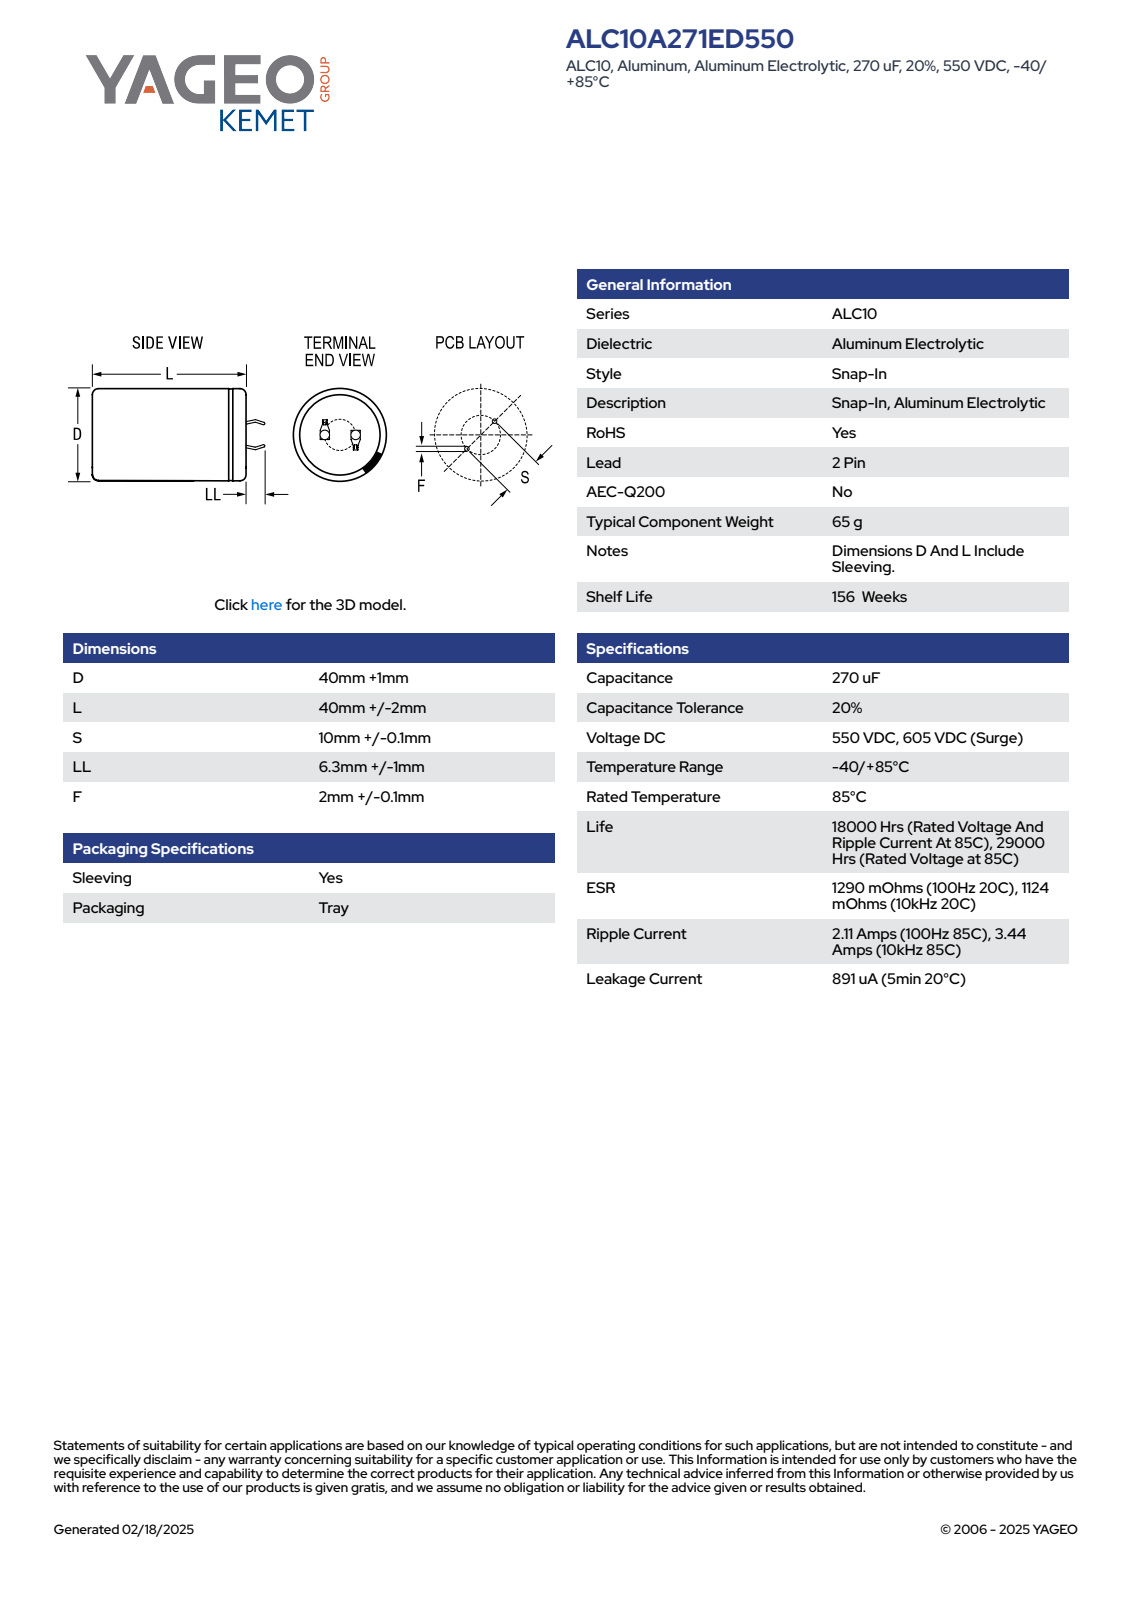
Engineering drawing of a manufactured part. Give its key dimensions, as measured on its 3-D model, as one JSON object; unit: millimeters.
{"part_name": "CARS_K2P_40X40_D41L42S10LL7.3F2.1", "step_written_by": "SolidWorks 2014 (AUTOMOTIVE_DESIGN)", "units": "millimeters", "bodies": {"solids": 1, "faces": 100, "planar": 52, "cylindrical": 9, "other": 39}, "overall_size": [49.29, 41, 41], "volume_mm3": 54666, "surface_area_mm2": 8033, "round_holes": [[36.28, 1]], "round_bosses_or_shafts": [[41, 1]], "partial_cylinders_radius": [[20.49, 1]], "face_to_face_distances": [41.99, 0.6, 42.49, 0.5, 7.08, 7.64, 0.75, 1.35, 7.68, 6.48]}
